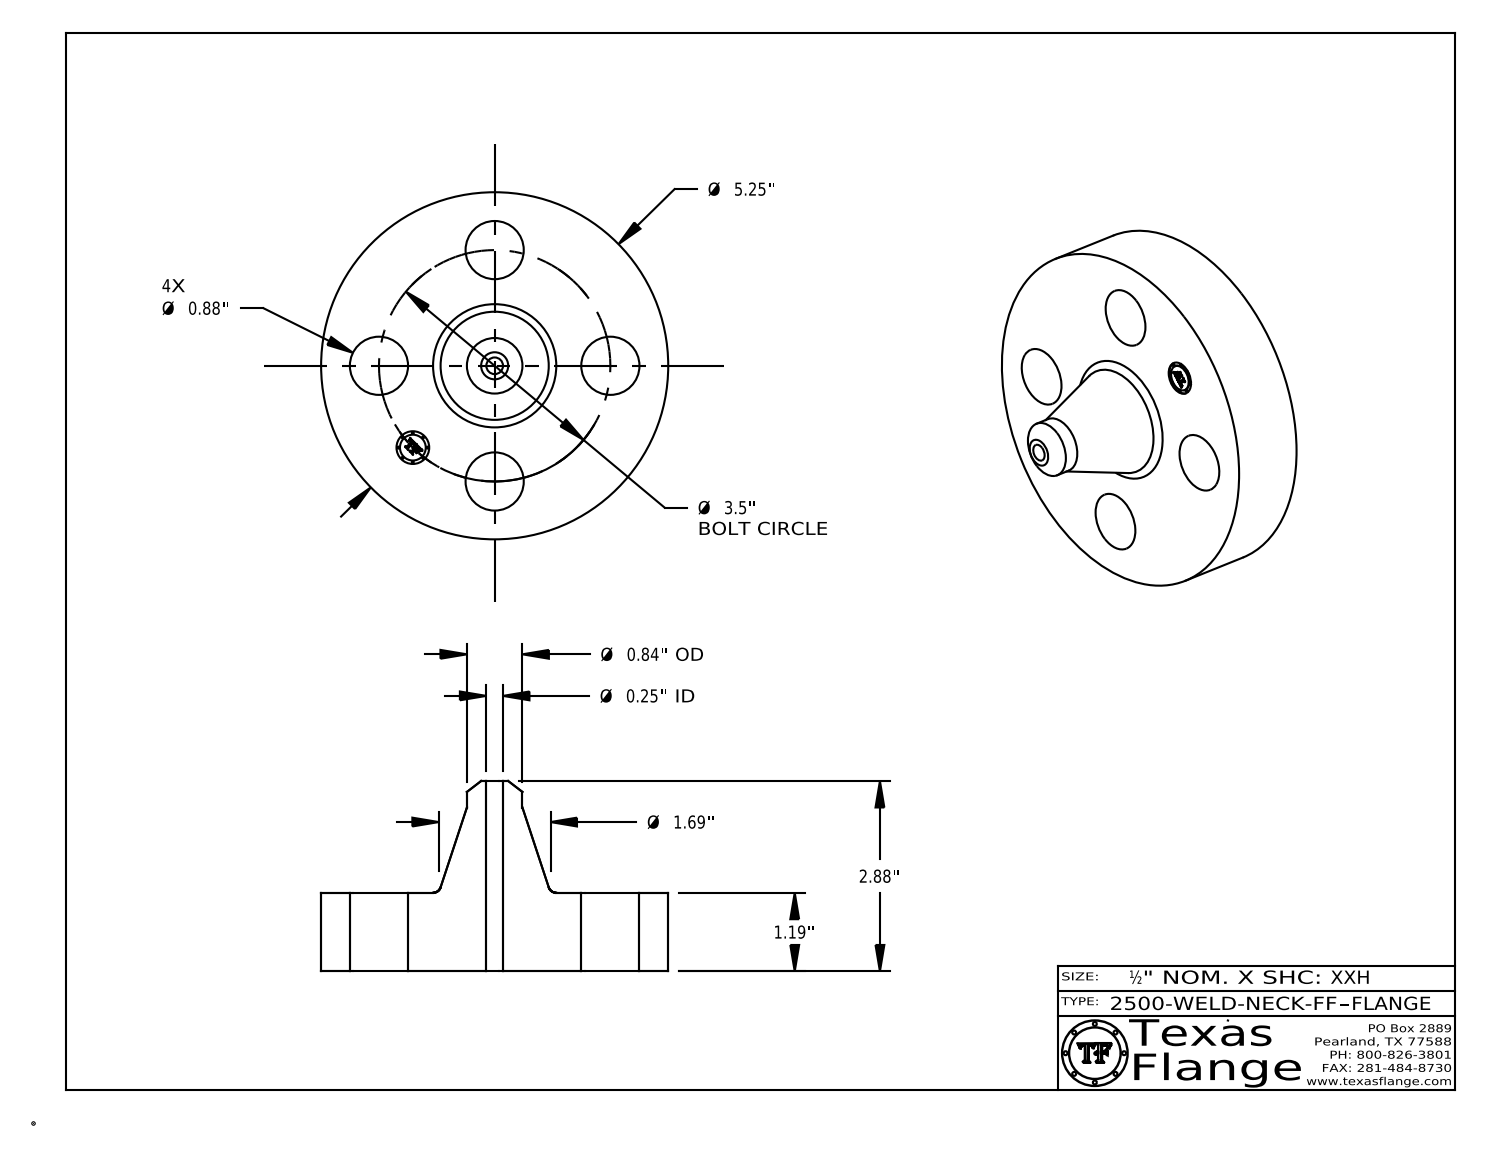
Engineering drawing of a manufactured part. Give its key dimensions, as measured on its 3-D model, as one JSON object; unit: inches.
{"part_name": "2500-WELD-NECK-FF", "step_written_by": "CATIA V5 STEP AP214 (AUTOMOTIVE_DESIGN)", "units": "inches", "bodies": {"solids": 1, "faces": 408, "planar": 368, "cylindrical": 34, "other": 6}, "overall_size": [5.25, 5.25, 2.88], "volume_in3": 24.59, "surface_area_in2": 77.81, "round_holes": [[0.88, 4], [0.252, 1], [0.495, 1]], "round_bosses_or_shafts": [[0.03, 8], [5.25, 1], [0.84, 1], [0.39, 1]], "face_to_face_distances": [1.19, 2.88, 1.69, 1.175, 0.015, 1.705, 0.148, 0.145, 0.027, 0.096], "hole_center_spacings": [1.75, 2.475, 1.339, 3.233, 3.5]}
